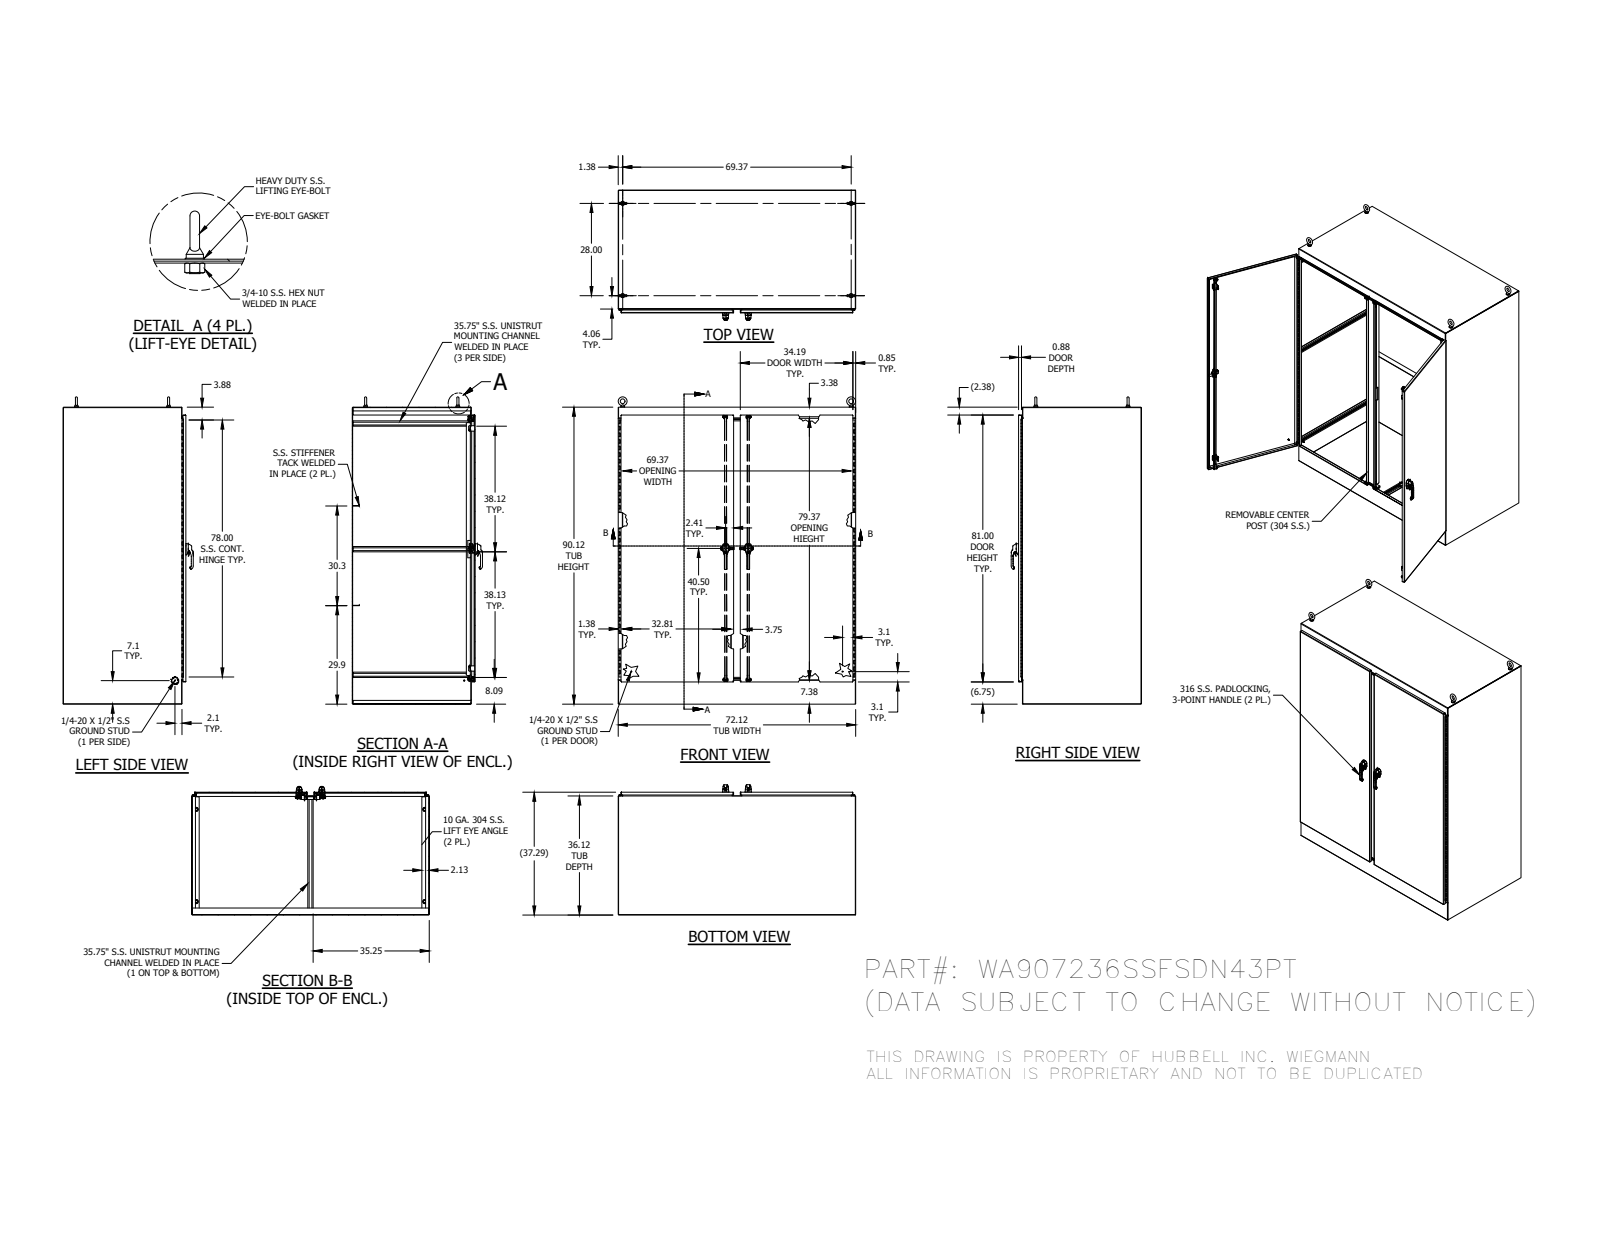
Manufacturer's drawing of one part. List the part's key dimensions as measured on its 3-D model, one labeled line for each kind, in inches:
Part name (STEP PRODUCT): HFW3026; 1000-02; WA9036SSFSDN43PTLS; WA907236SSFSDN43PT (+8 more)
STEP written by: SolidWorks 2014 (AUTOMOTIVE_DESIGN)
Units: inches
Bodies: 139 solids, 7572 faces (2824 planar, 2844 cylindrical, 1904 other)
Overall size (bounding box): 93.248 × 72.125 × 39.541
Volume: 3 607 in³ · Surface area: 58 696 in²
Round holes (diameter × count): ⌀0.262 ×16, ⌀0.375 ×16, ⌀0.187 ×8, ⌀0.213 ×6, ⌀0.25 ×6, ⌀0.281 ×6, ⌀0.196 ×4, ⌀0.241 ×4, ⌀0.252 ×4, ⌀0.281 ×4, ⌀0.315 ×4, ⌀0.4 ×4
Round bosses / shafts (diameter × count): ⌀0.25 ×7, ⌀1 ×6, ⌀0.533 ×6, ⌀0.236 ×6, ⌀1.25 ×4, ⌀1.12 ×4, ⌀0.75 ×4, ⌀0.563 ×4
Partial cylindrical surfaces — rounded edges, fillets, slot ends (radius × count): R0.02 ×350, R0.012 ×213, R0.019 ×44, R0.125 ×44, R0.05 ×34, R0.079 ×28, R0.025 ×24, R0.059 ×24
Main face-to-face distances: 0.125, 0.125, 72, 37.167, 90, 71.875, 72.125, 37.165, 37.04, 37.042
Hole centre spacings: 72.49, 73.24, 26, 0.38, 0.38, 8.667, 0.76, 17.333
